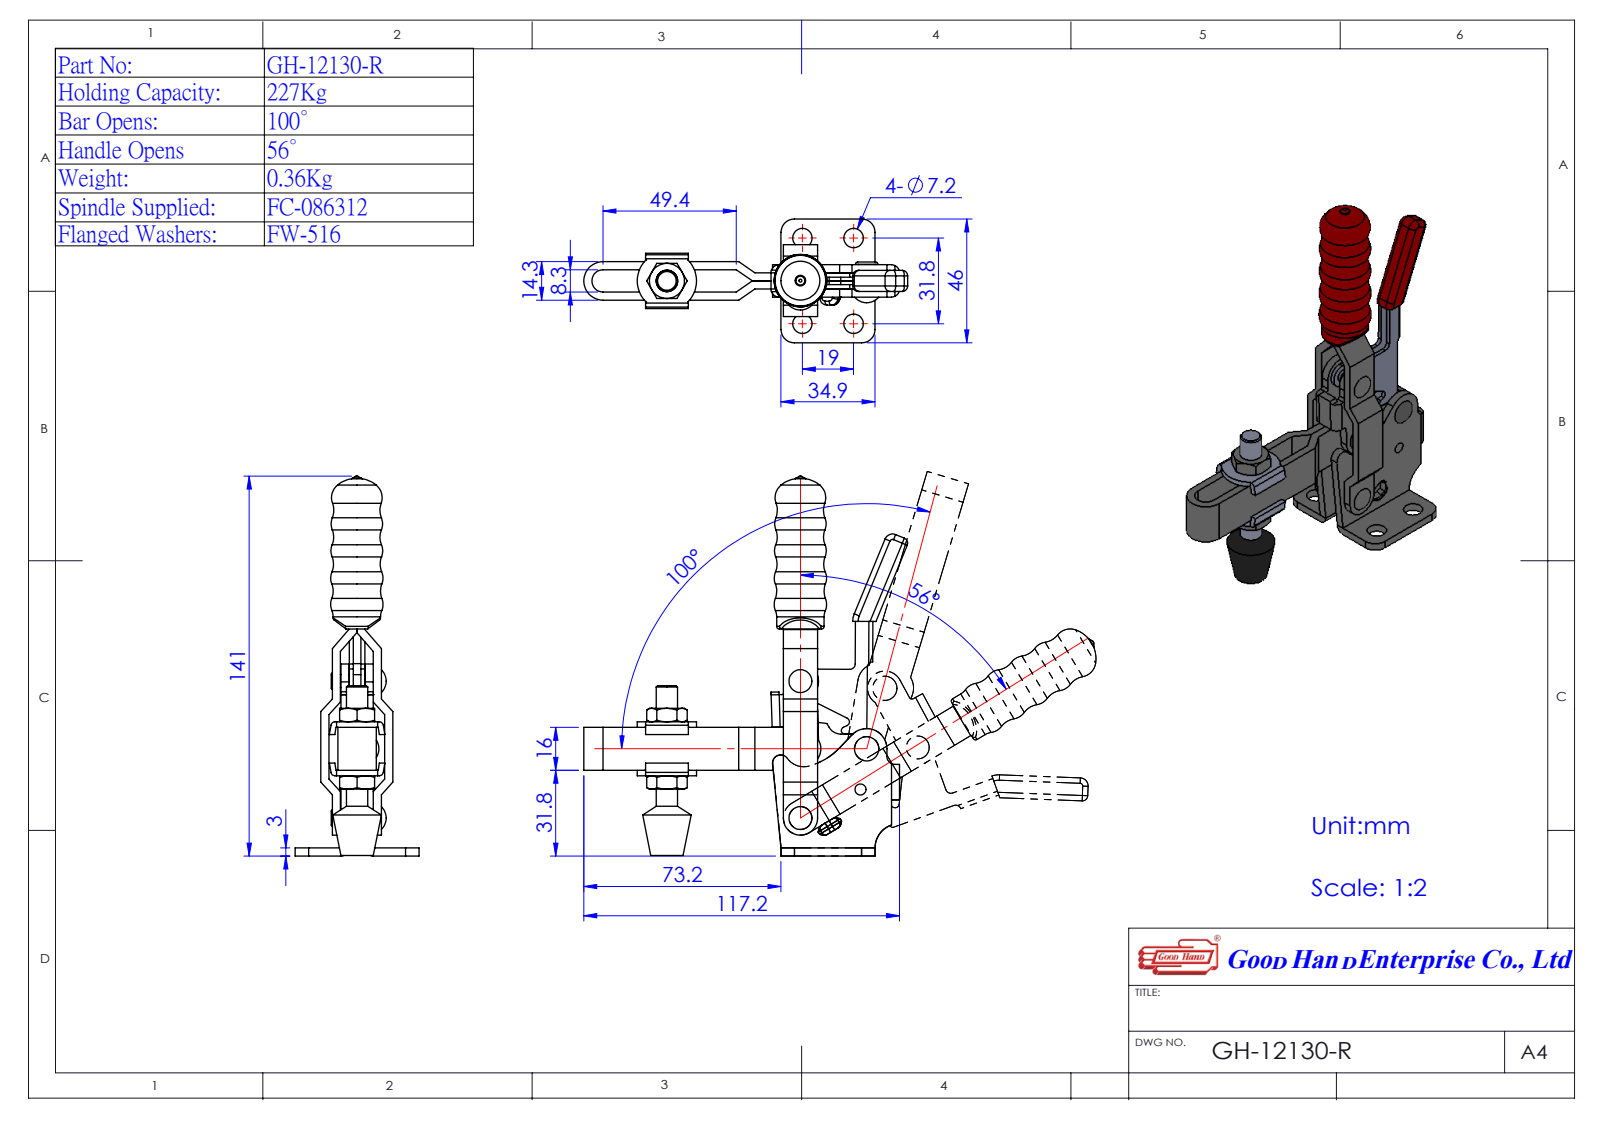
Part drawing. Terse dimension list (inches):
name: GH-12130-R
written by: SolidWorks 2016 (AUTOMOTIVE_DESIGN)
unit: in
bodies: 6 solids, 419 faces (191 planar, 133 cylindrical, 95 other)
size: 5.557 × 4.72 × 1.811
volume: 3.667 in³; area: 61.12 in²
holes: 4× ⌀0.157, 4× ⌀0.283, 1× ⌀0.118
bosses: 2× ⌀0.252, 2× ⌀0.248, 1× ⌀0.693, 1× ⌀0.312
rounds: 9× R0.079, 8× R0.059, 5× R0.118, 5× R0.295, 4× R0.197, 3× R0.039, 2× R0.252, 2× R0.354
face distances: 0.118, 0.236, 0.354, 0.045, 0.163, 0.281, 0.4, 0.167, 0.472, 0.518
hole spacings: 0.748, 1.252, 1.458, 0.601, 0.921, 0.972, 0.989, 1.013
